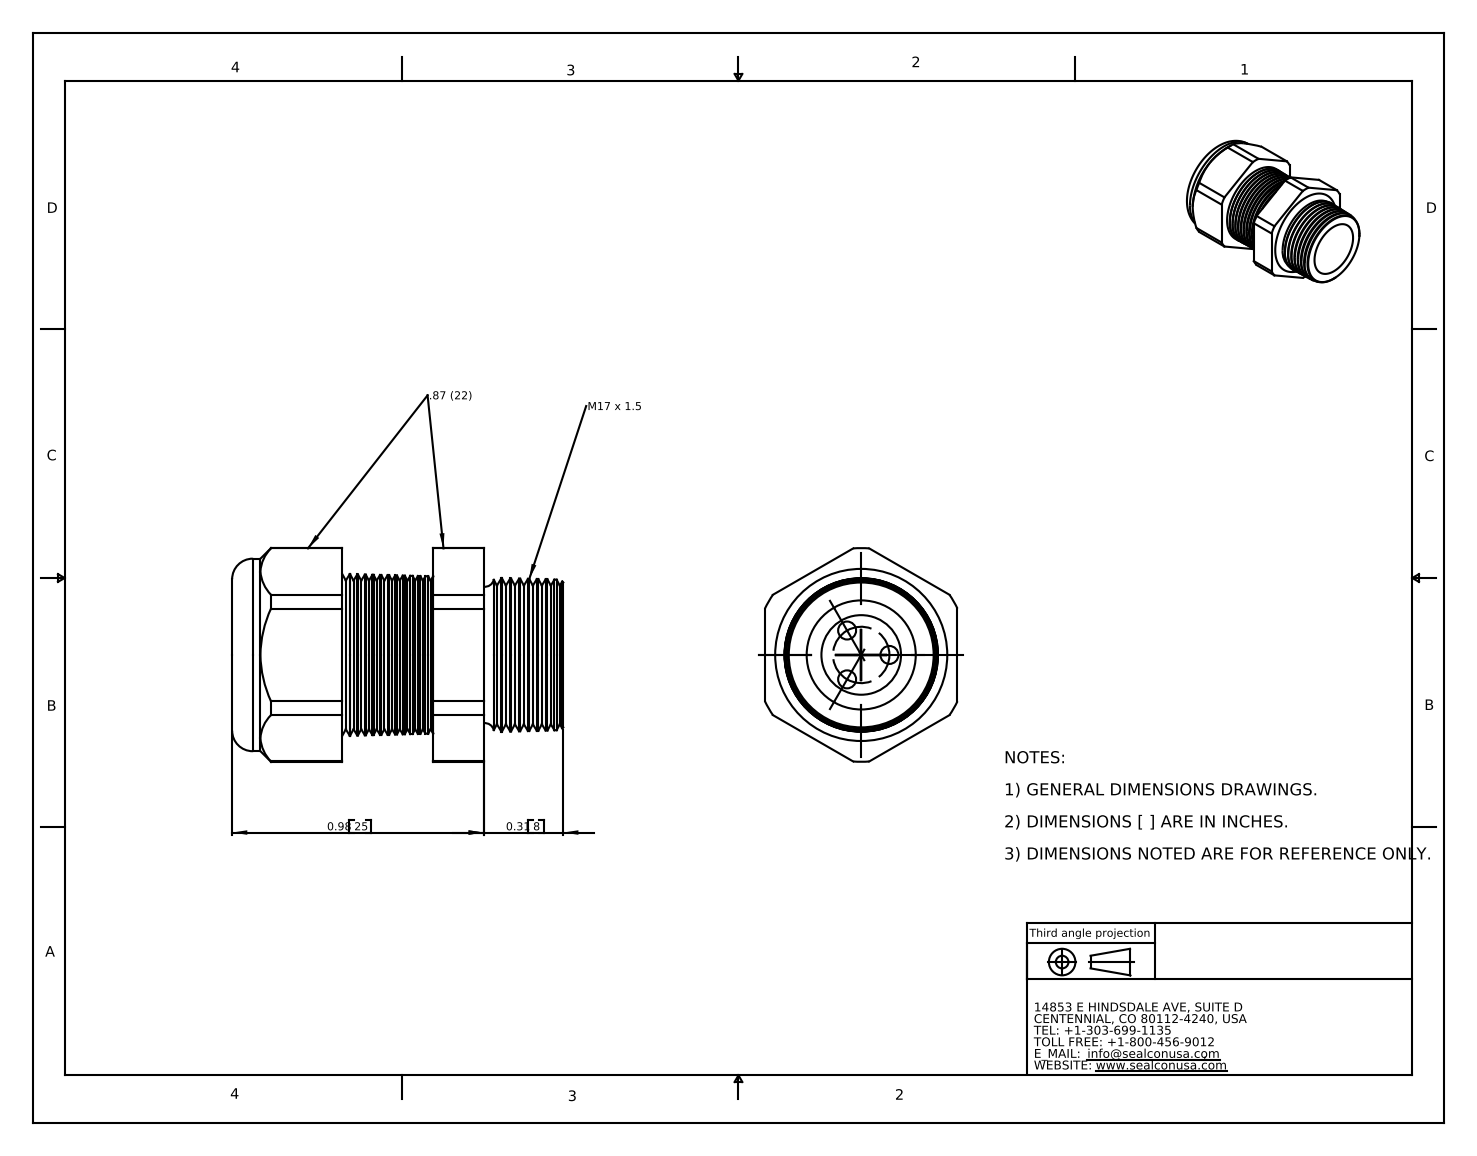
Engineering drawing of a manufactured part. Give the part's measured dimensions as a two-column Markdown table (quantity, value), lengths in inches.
| quantity | value |
| --- | --- |
| part name | CD17M4-GY |
| STEP written by | SolidWorks 2007 (CONFIG_CONTROL_DESIGN) |
| units | inches |
| bodies | 2 solids, 185 faces (21 planar, 26 cylindrical, 138 other) |
| overall size | 1.29 × 0.833 × 0.75 |
| volume | 0.355 in³ |
| surface area | 6.662 in² |
| round holes (diameter × count) | 0.07 × 3, 0.29 × 1, 0.31 × 1 |
| round bosses / shafts (diameter × count) | 0.75 × 1 |
| partial cylindrical surfaces (radius × count) | 0.416 × 1 |
| main face-to-face distances | 0.75, 0.75, 0.783, 0.429, 0.354, 0.98, 0.551, 0.197, 1.29, 0.861 |
| hole center spacings | 0.191, 0.11, 0.11 |
